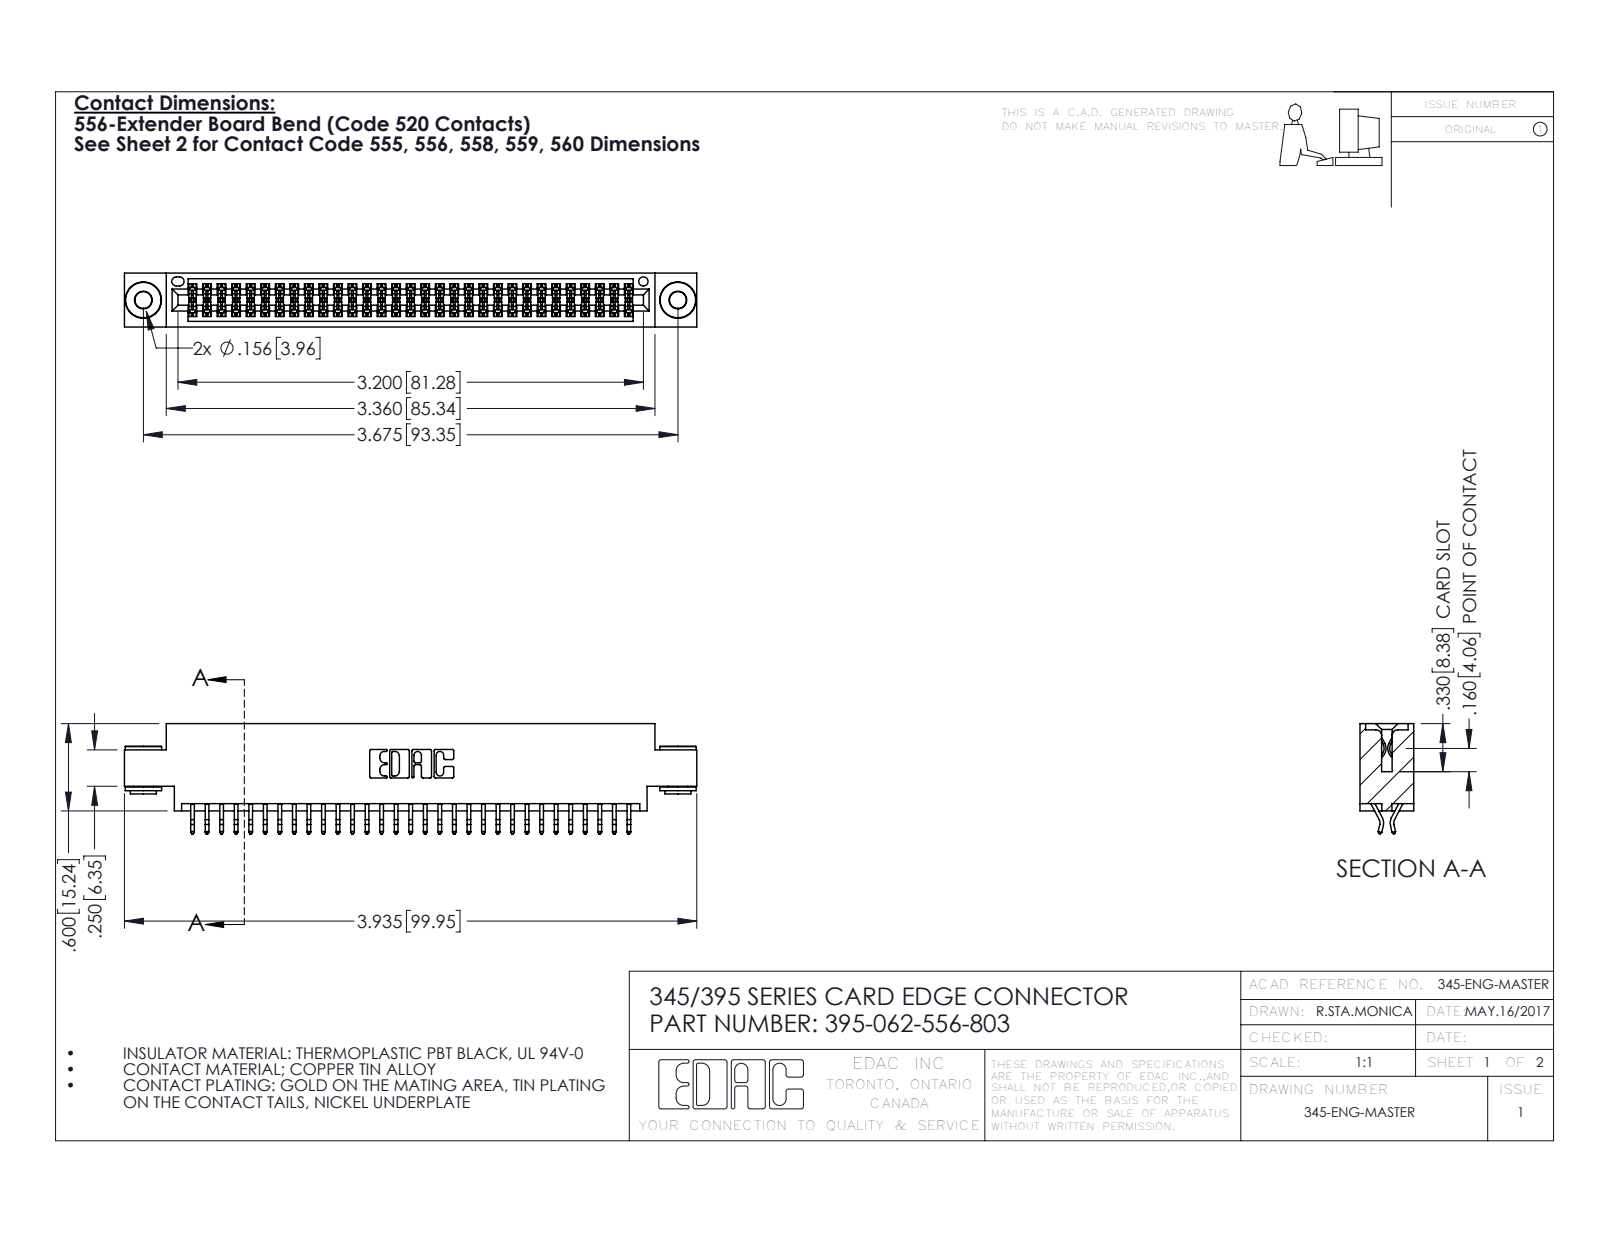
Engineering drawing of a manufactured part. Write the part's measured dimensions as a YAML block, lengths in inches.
part_name: "345 Part_0.170 Offset - 0.156 Dia-TH; 345-250-002_345-250-002-102; 345-292-001_556 Tail; 395-062-556-803"
step_written_by: "SolidWorks 2016 (CONFIG_CONTROL_DESIGN)"
units: inches
bodies: {solids: 65, faces: 3640, planar: 2388, cylindrical: 1244, other: 8}
overall_size: [3.935, 0.757, 0.37]
volume: 0.58
surface_area: 21.92
round_holes:
  - {diameter: 0.116, count: 2}
  - {diameter: 0.156, count: 2}
  - {diameter: 0.064, count: 1}
round_bosses_or_shafts:
  - {diameter: 0.25, count: 2}
  - {diameter: 0.18, count: 2}
  - {diameter: 0.136, count: 2}
partial_cylinders:
  - {radius: 0.006, count: 93}
  - {radius: 0.01, count: 22}
  - {radius: 0.007, count: 6}
  - {radius: 0.031, count: 6}
  - {radius: 0.026, count: 3}
  - {radius: 0.01, count: 2}
  - {radius: 0.014, count: 2}
  - {radius: 0.019, count: 2}
face_to_face_distances: [0.072, 0.298, 0.37, 0.2, 0.025, 0.098, 0.272, 0.225, 0.175, 0.149]
hole_center_spacings: [0.27, 3.44, 3.675]
